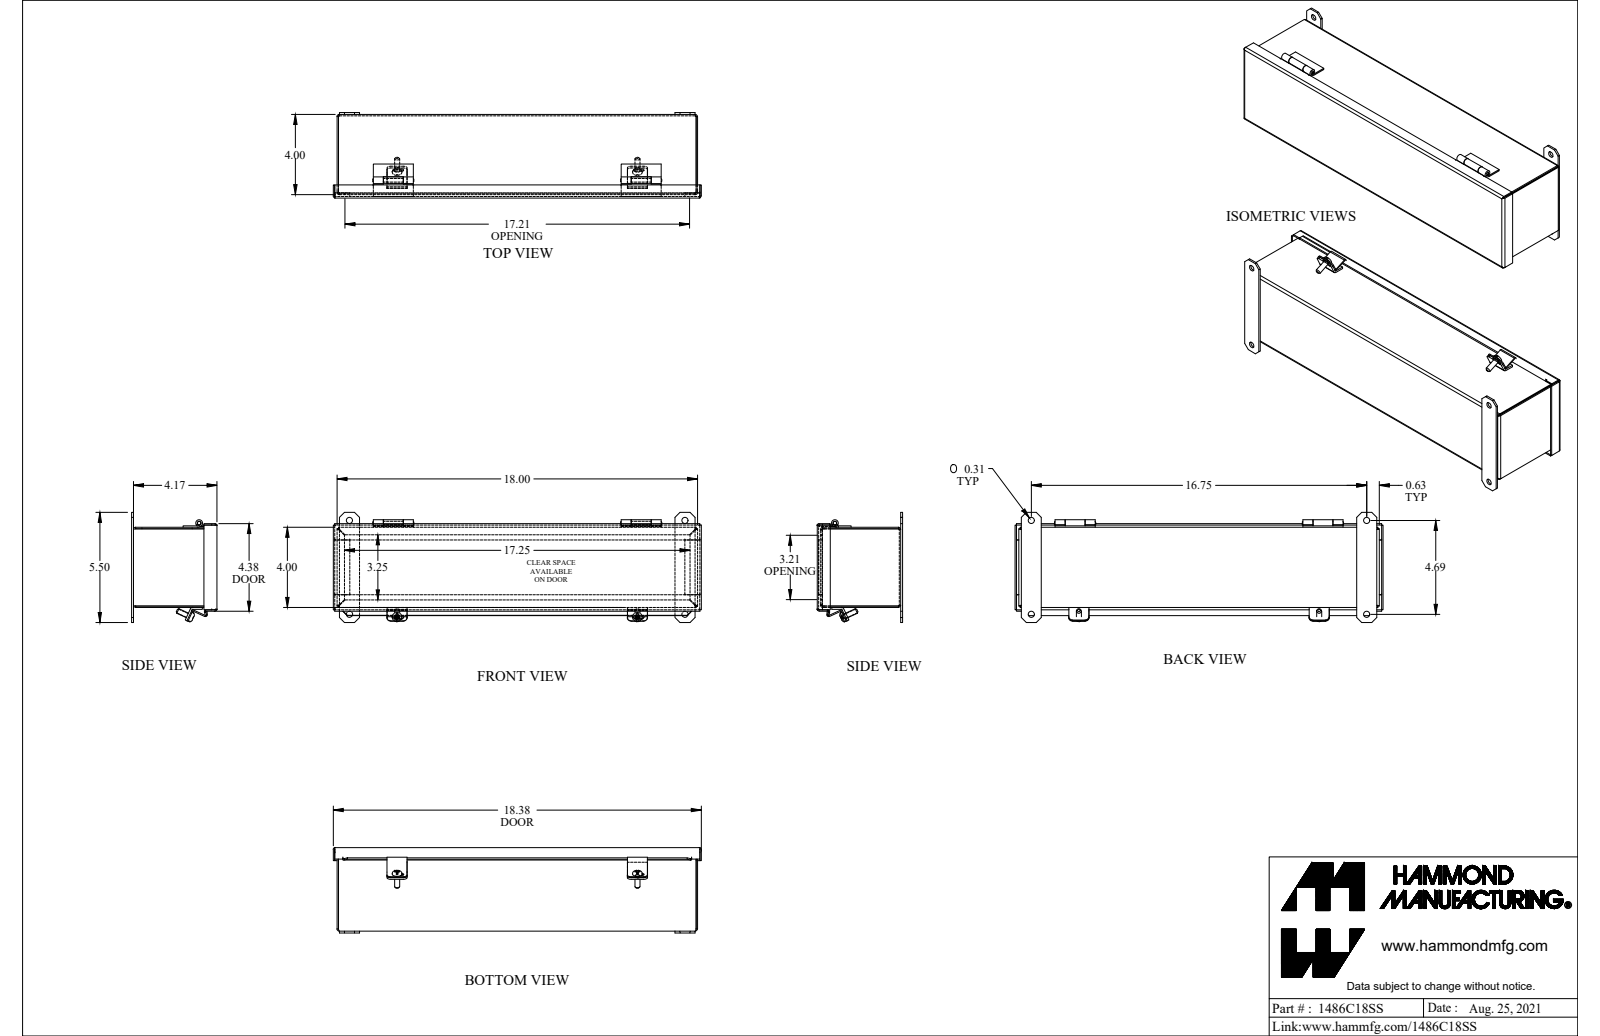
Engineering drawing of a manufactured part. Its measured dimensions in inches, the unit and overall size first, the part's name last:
Units: inches
Overall size (bounding box): 18.375 × 5.5 × 4.267
Round holes (diameter × count): ⌀0.313 ×4, ⌀0.213 ×2, ⌀0.187 ×1
Round bosses / shafts (diameter × count): ⌀0.483 ×2, ⌀0.25 ×2, ⌀0.337 ×1, ⌀0.18 ×1
Partial cylindrical surfaces — rounded edges, fillets, slot ends (radius × count): R0.036 ×13, R0.108 ×13, R0.25 ×12, R0.188 ×8, R0.01 ×4, R0.03 ×4, R0.141 ×4, R0.029 ×2
Main face-to-face distances: 0.072, 3.928, 4.1, 3.856, 4, 0.187, 4.028, 4.172, 0.259, 3.913
Hole centre spacings: 4.688, 12, 16.75, 16.75, 17.393, 17.394
Volume: 34.06 in³ · Surface area: 839.4 in²
Bodies: 7 solids, 418 faces (270 planar, 112 cylindrical, 36 other)
Part name (STEP PRODUCT): 1486C18SS
STEP written by: SolidWorks 2021 (AUTOMOTIVE_DESIGN)
